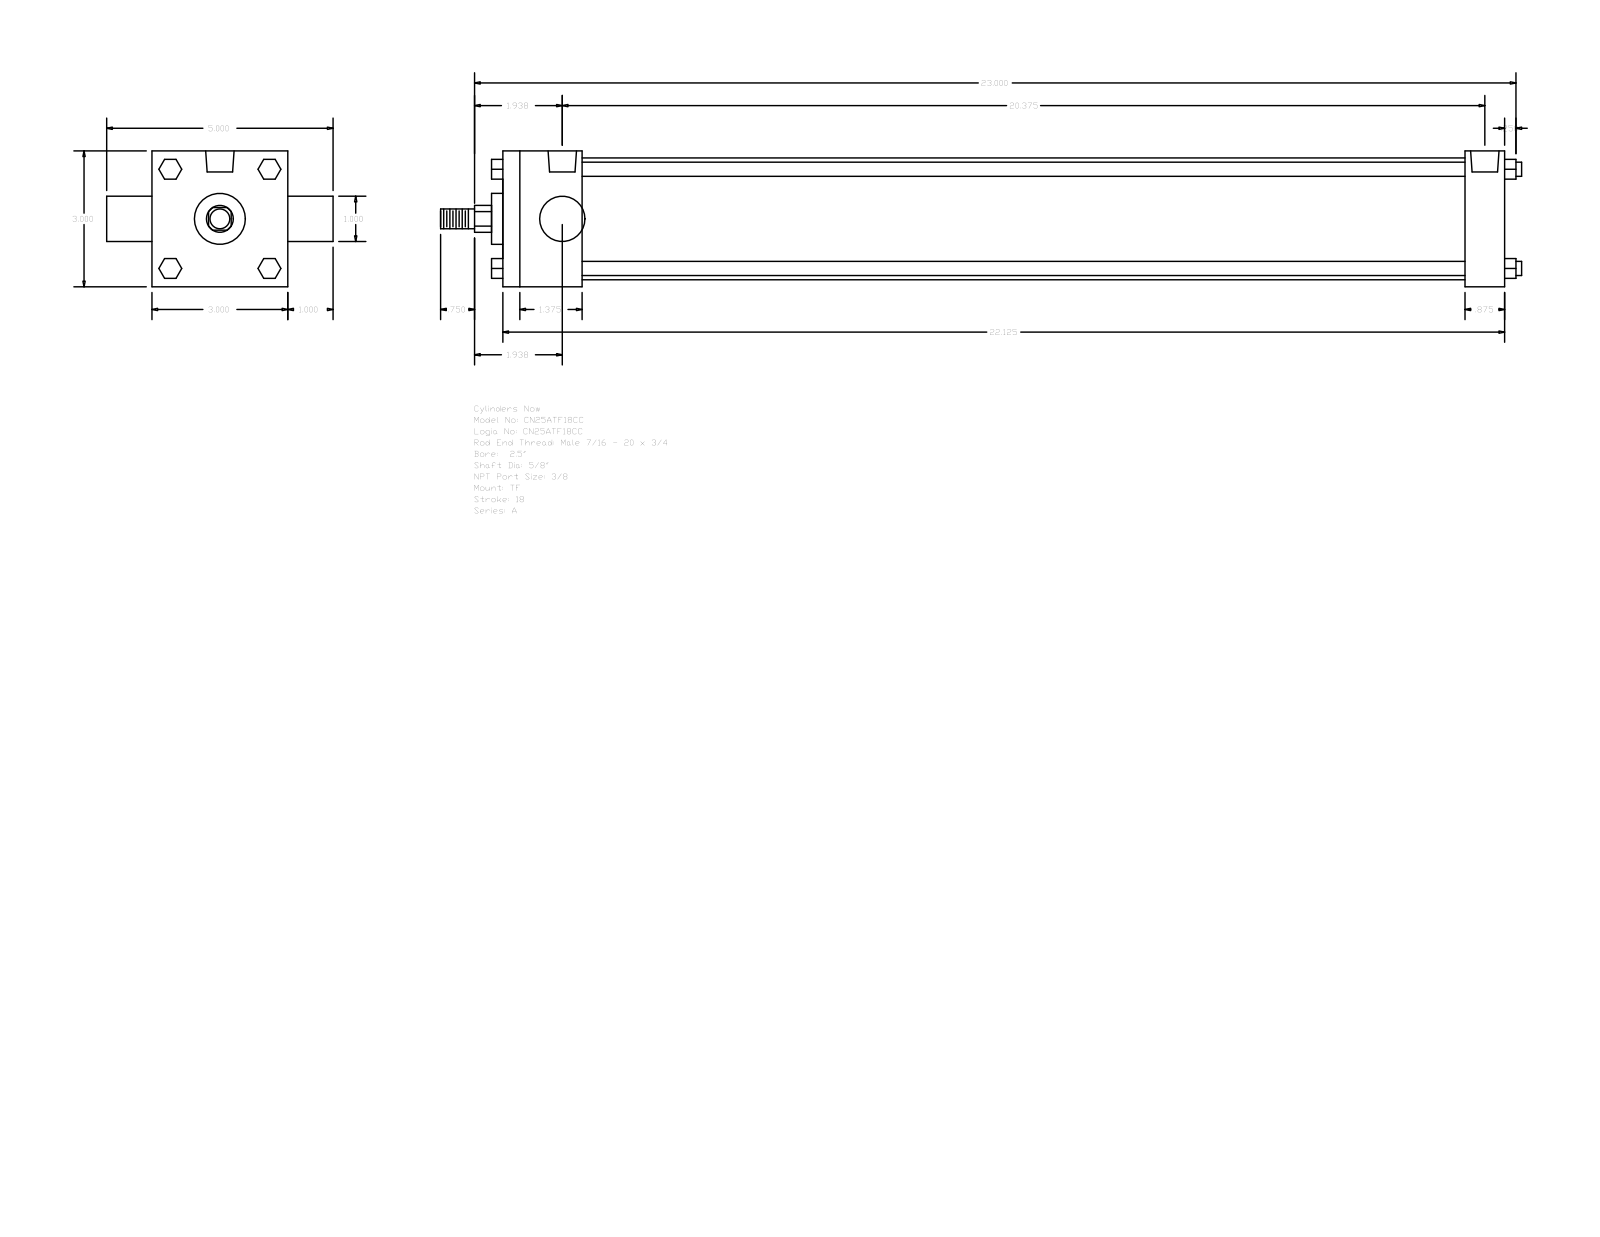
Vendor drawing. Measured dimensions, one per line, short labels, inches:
name: A_TF__0250_0.625
written by: GSSL Pune (CONFIG_CONTROL_DESIGN)
unit: in
bodies: 0 solids, 120 faces (92 planar, 28 cylindrical, 0 other)
size: 23.875 × 5 × 3
holes: 3× ⌀0.219, 2× ⌀0.627
bosses: 4× ⌀0.313, 1× ⌀2.69, 1× ⌀1.125, 1× ⌀1, 1× ⌀0.625, 1× ⌀0.437
rounds: 1× R0.297
face distances: 3, 22.125, 1.75, 21.25, 19.5, 20.375, 0.875, 1, 4, 0.25
hole spacings: 0.094, 20.469, 20.375, 20.563
